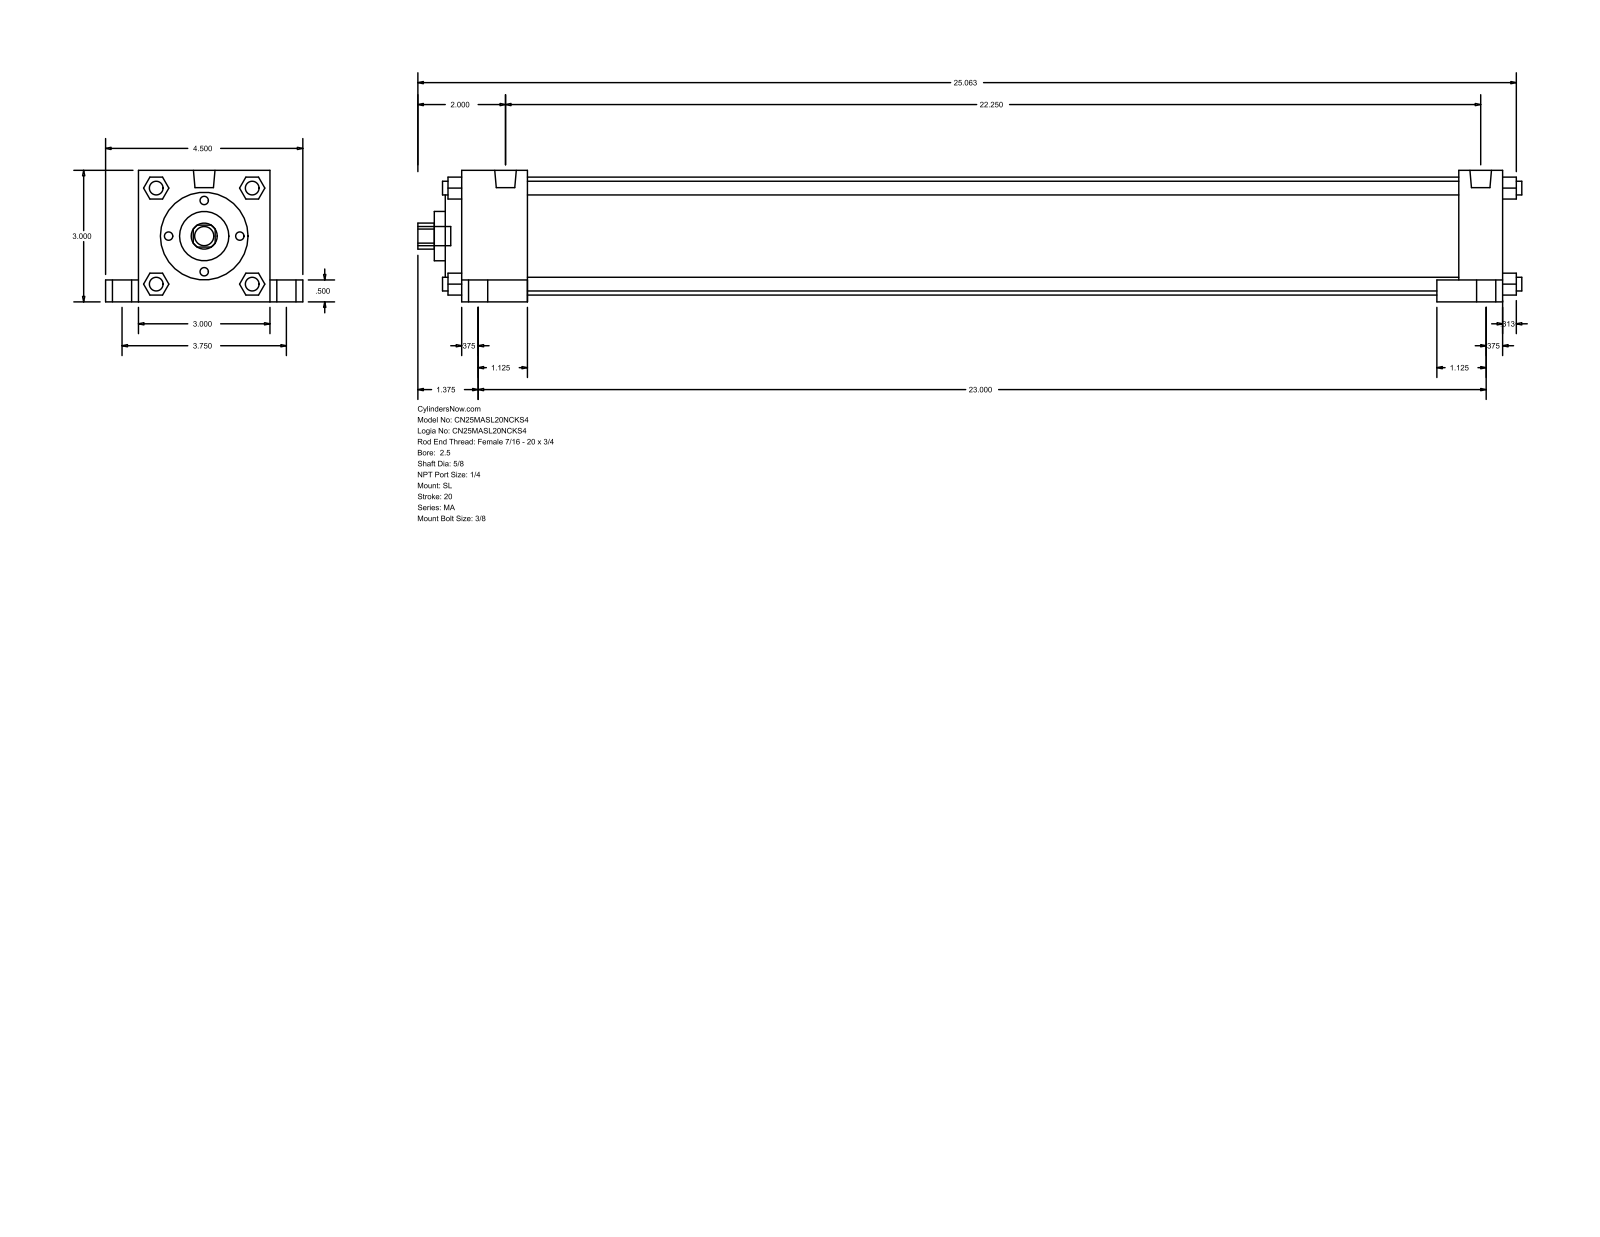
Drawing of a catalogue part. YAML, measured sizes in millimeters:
part_name: "MA_SL__0250_0.625"
step_written_by: "GSSL Pune (CONFIG_CONTROL_DESIGN)"
units: millimeters
bodies: {solids: 0, faces: 150, planar: 113, cylindrical: 37, other: 0}
overall_size: [639.76, 114.3, 76.2]
round_holes:
  - {diameter: 15.88, count: 1}
  - {diameter: 28.57, count: 1}
  - {diameter: 50.8, count: 1}
  - {diameter: 68.33, count: 1}
round_bosses_or_shafts:
  - {diameter: 7.94, count: 8}
  - {diameter: 11.11, count: 5}
  - {diameter: 17.46, count: 4}
  - {diameter: 12.49, count: 2}
partial_cylinders:
  - {radius: 7.54, count: 1}
face_to_face_distances: [76.2, 603.25, 12.7, 539.75, 25.4, 38.1, 565.15, 577.85, 19.05, 63.5]
